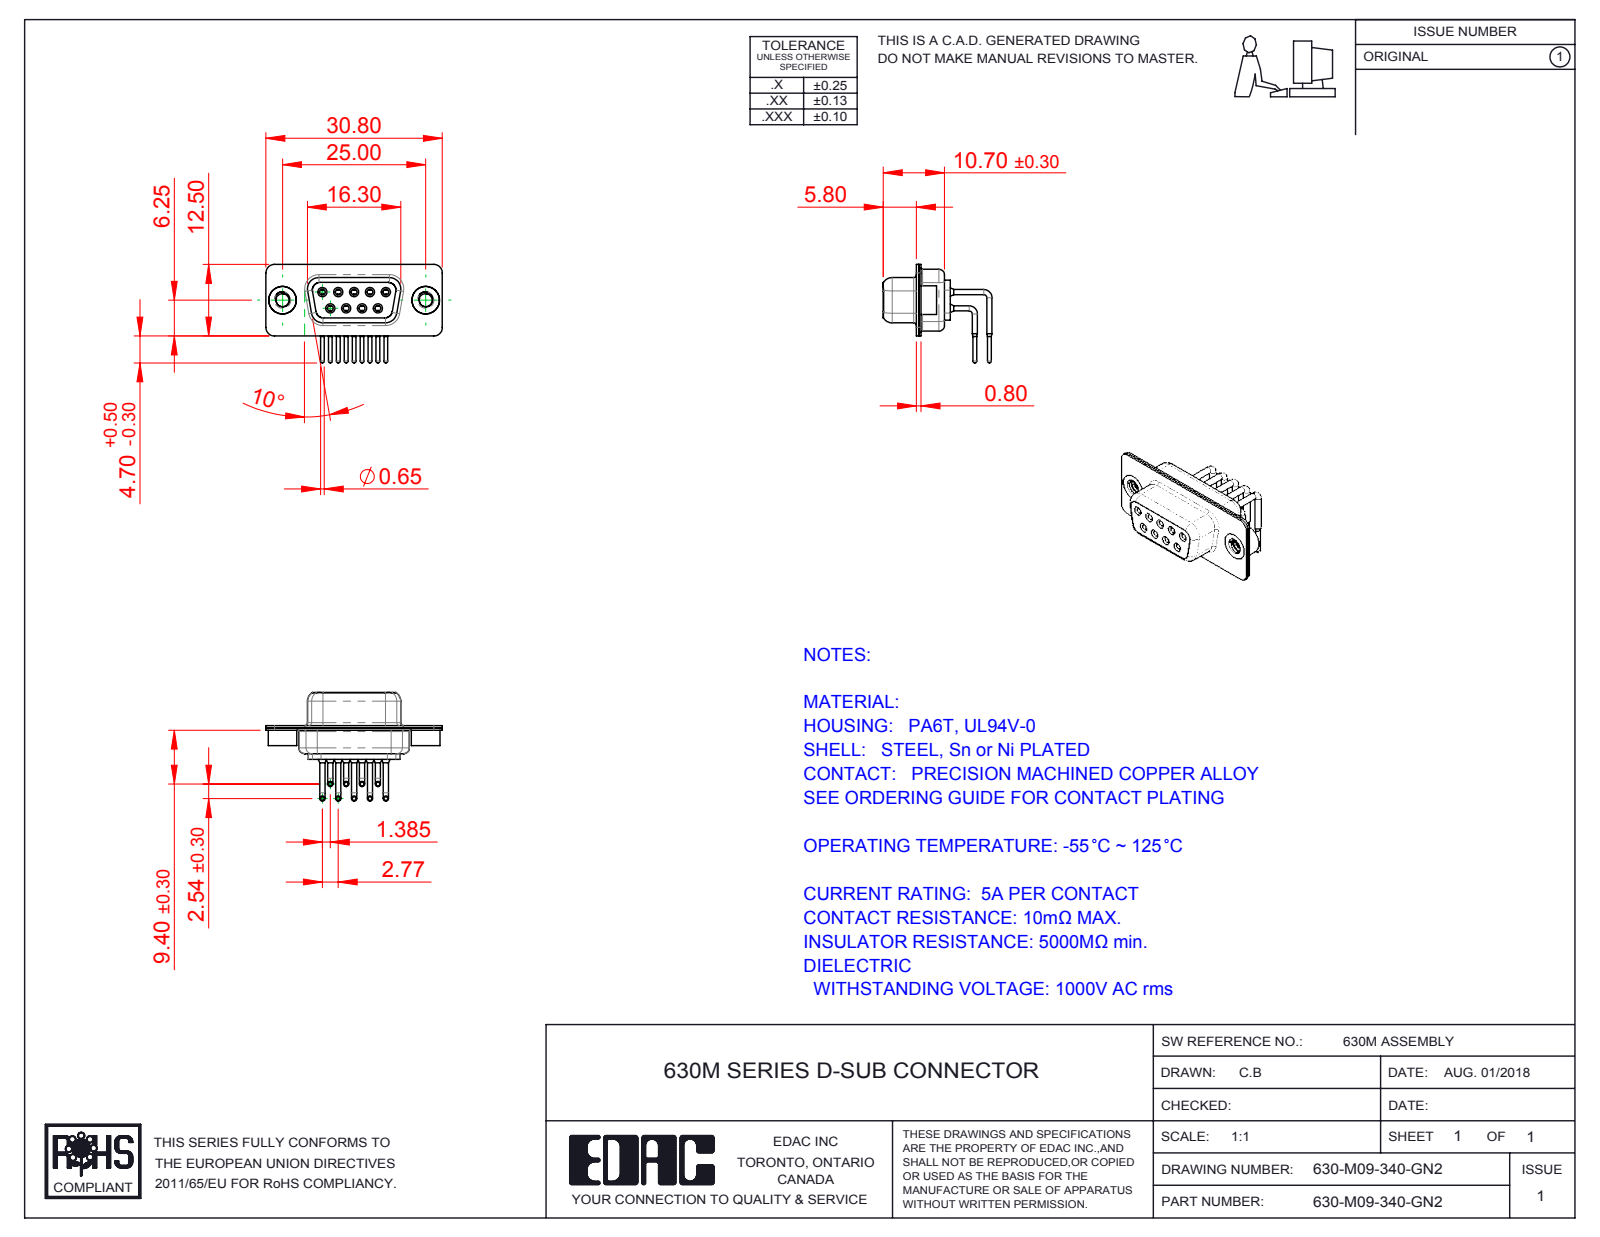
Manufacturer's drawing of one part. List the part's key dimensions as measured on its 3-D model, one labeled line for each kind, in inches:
Part name (STEP PRODUCT): 630M Housing_09 Contacts; 630M Contact Row 1; 630M Contact Row 2; 630M 4-40 Threaded Rivet (+3 more)
STEP written by: SolidWorks 2016 (CONFIG_CONTROL_DESIGN)
Units: inches
Bodies: 14 solids, 756 faces (202 planar, 344 cylindrical, 210 other)
Overall size (bounding box): 1.213 × 0.748 × 0.677
Volume: 0.107 in³ · Surface area: 7.192 in²
Round holes (diameter × count): ⌀0.039 ×9, ⌀0.043 ×9, ⌀0.067 ×9, ⌀0.071 ×9, ⌀0.079 ×9, ⌀0.089 ×2, ⌀0.157 ×2, ⌀0.189 ×2
Round bosses / shafts (diameter × count): ⌀0.035 ×18, ⌀0.063 ×9, ⌀0.059 ×9, ⌀0.026 ×9, ⌀0.197 ×2, ⌀0.193 ×2
Partial cylindrical surfaces — rounded edges, fillets, slot ends (radius × count): R0.059 ×16, R0.079 ×12, R0.053 ×8, R0.063 ×8, R0.01 ×4, R0.02 ×4, R0.024 ×4, R0.026 ×4
Main face-to-face distances: 0.016, 0.031, 0.057, 0.091, 0.352, 0.244, 0.335, 0.075, 0.033, 0.368
Hole centre spacings: 0.124, 0.109, 0.218, 0.198, 0.198, 0.327, 0.28, 0.294
